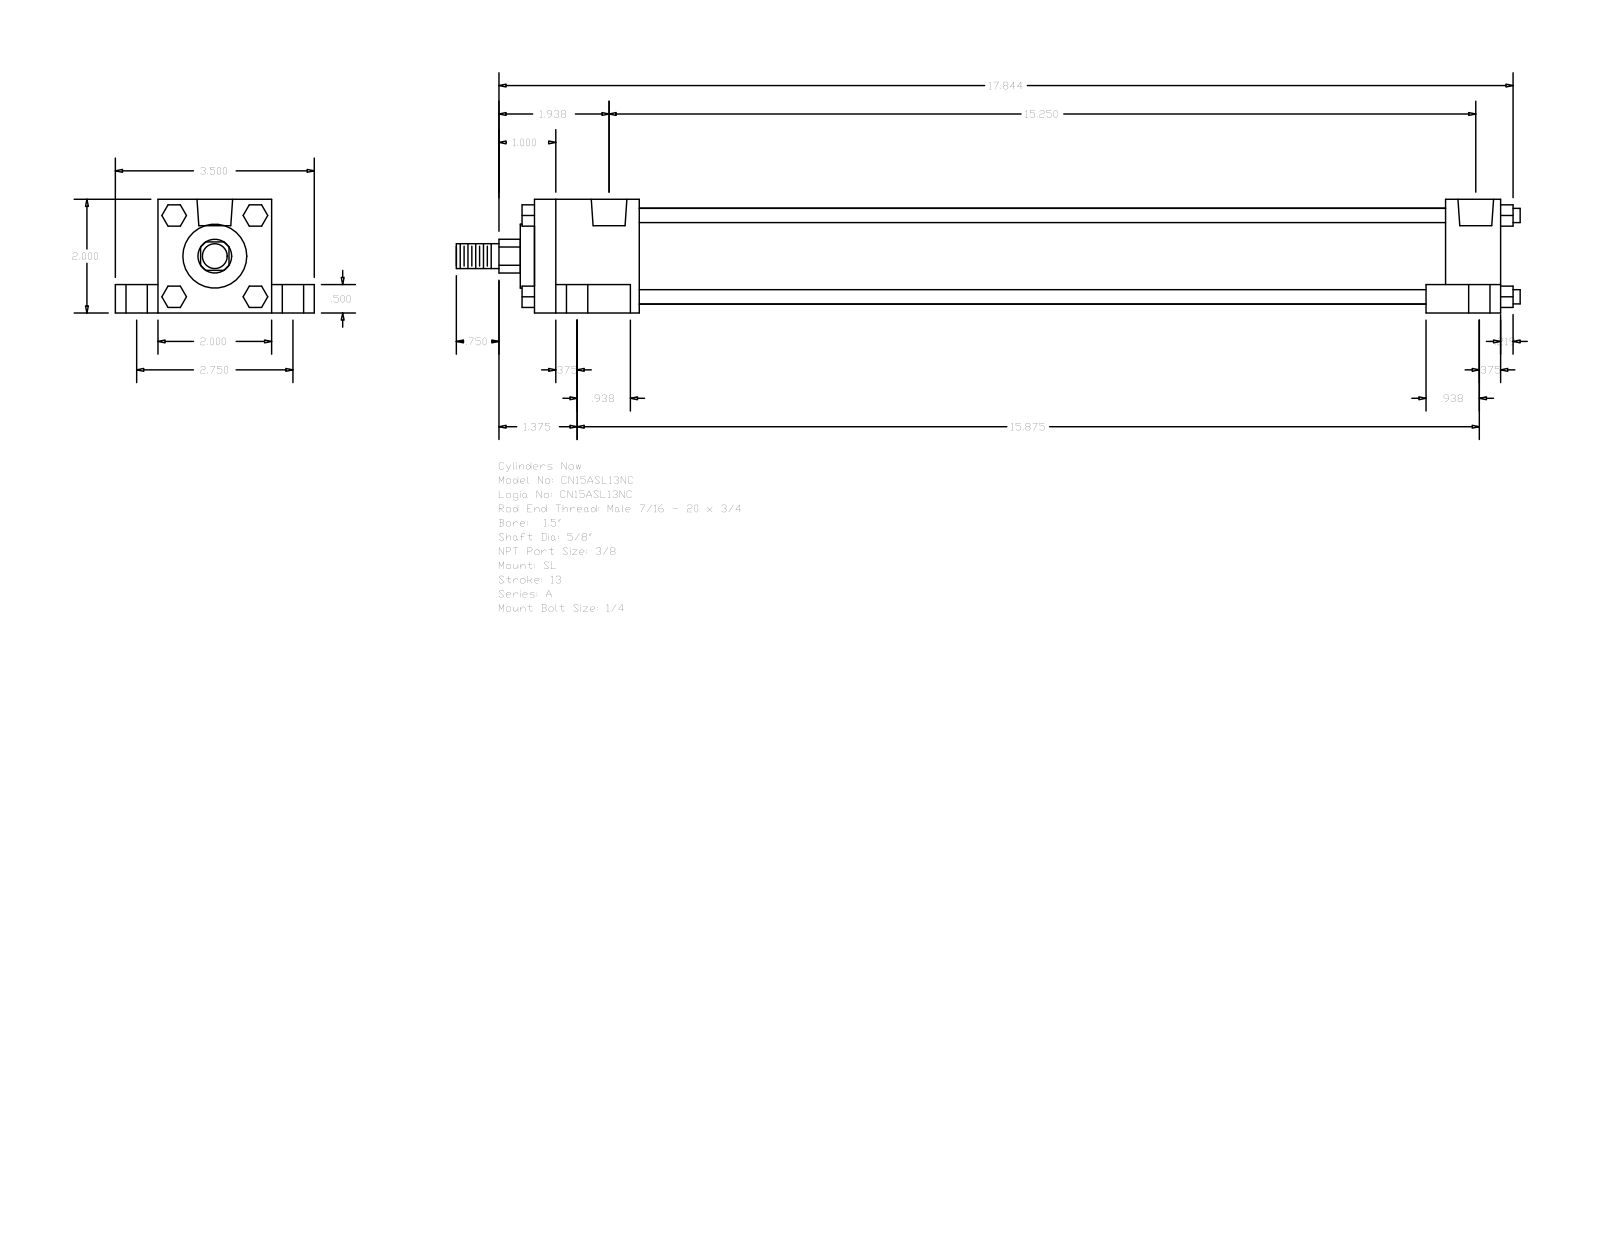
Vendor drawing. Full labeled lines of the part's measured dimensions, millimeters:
Part name (STEP PRODUCT): A_SL__0150_0.625
STEP written by: GSSL Pune (CONFIG_CONTROL_DESIGN)
Units: millimetres
Bodies: 0 solids, 148 faces (112 planar, 36 cylindrical, 0 other)
Overall size (bounding box): 475.46 × 88.9 × 50.8
Round holes (diameter × count): ⌀5.56 ×4, ⌀9.53 ×4, ⌀15.88 ×4, ⌀15.93 ×2
Round bosses / shafts (diameter × count): ⌀6.35 ×4, ⌀42.93 ×1, ⌀28.57 ×1, ⌀15.88 ×1, ⌀11.11 ×1
Partial cylindrical surfaces — rounded edges, fillets, slot ends (radius × count): R7.54 ×1
Main face-to-face distances: 50.8, 19.05, 38.1, 12.7, 69.85, 431.8, 9.52, 33.34, 407.19, 24.61
Hole centre spacings: 3.97, 34.96, 35.36, 37.73, 39.41, 69.84, 379.41, 383.38
